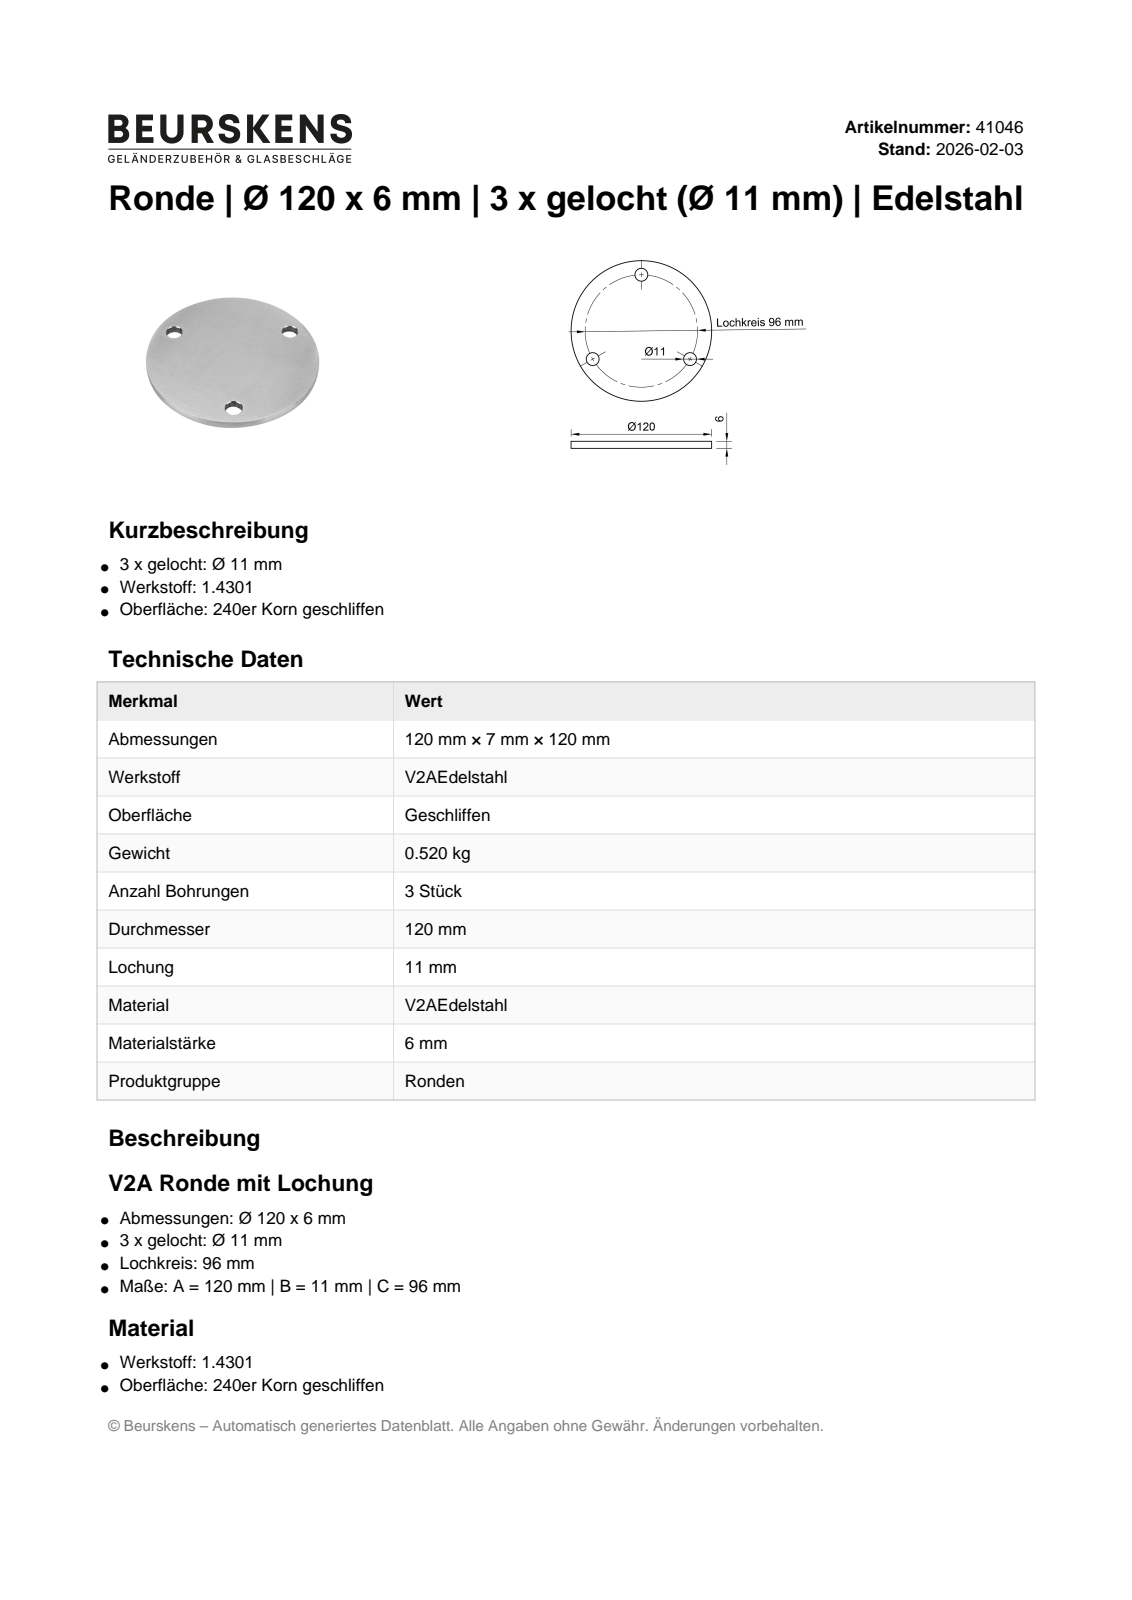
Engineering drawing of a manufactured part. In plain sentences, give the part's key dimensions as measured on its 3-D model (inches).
The part is named "41046". Its 3-D file was written by "Autodesk Inventor 2022 (AUTOMOTIVE_DESIGN)". It is 1 solid with 6 faces: 2 planar, 4 cylindrical and 0 other. Overall it measures 4.724 by 4.724 by 0.236 inches. Its volume is 4.037 cubic inches and its surface area 38.65 square inches. Round holes: 3 of diameter 0.433. Round bosses or shafts: 1 of diameter 4.724. The main face-to-face distances are 0.236. The hole center spacings are 3.273.
